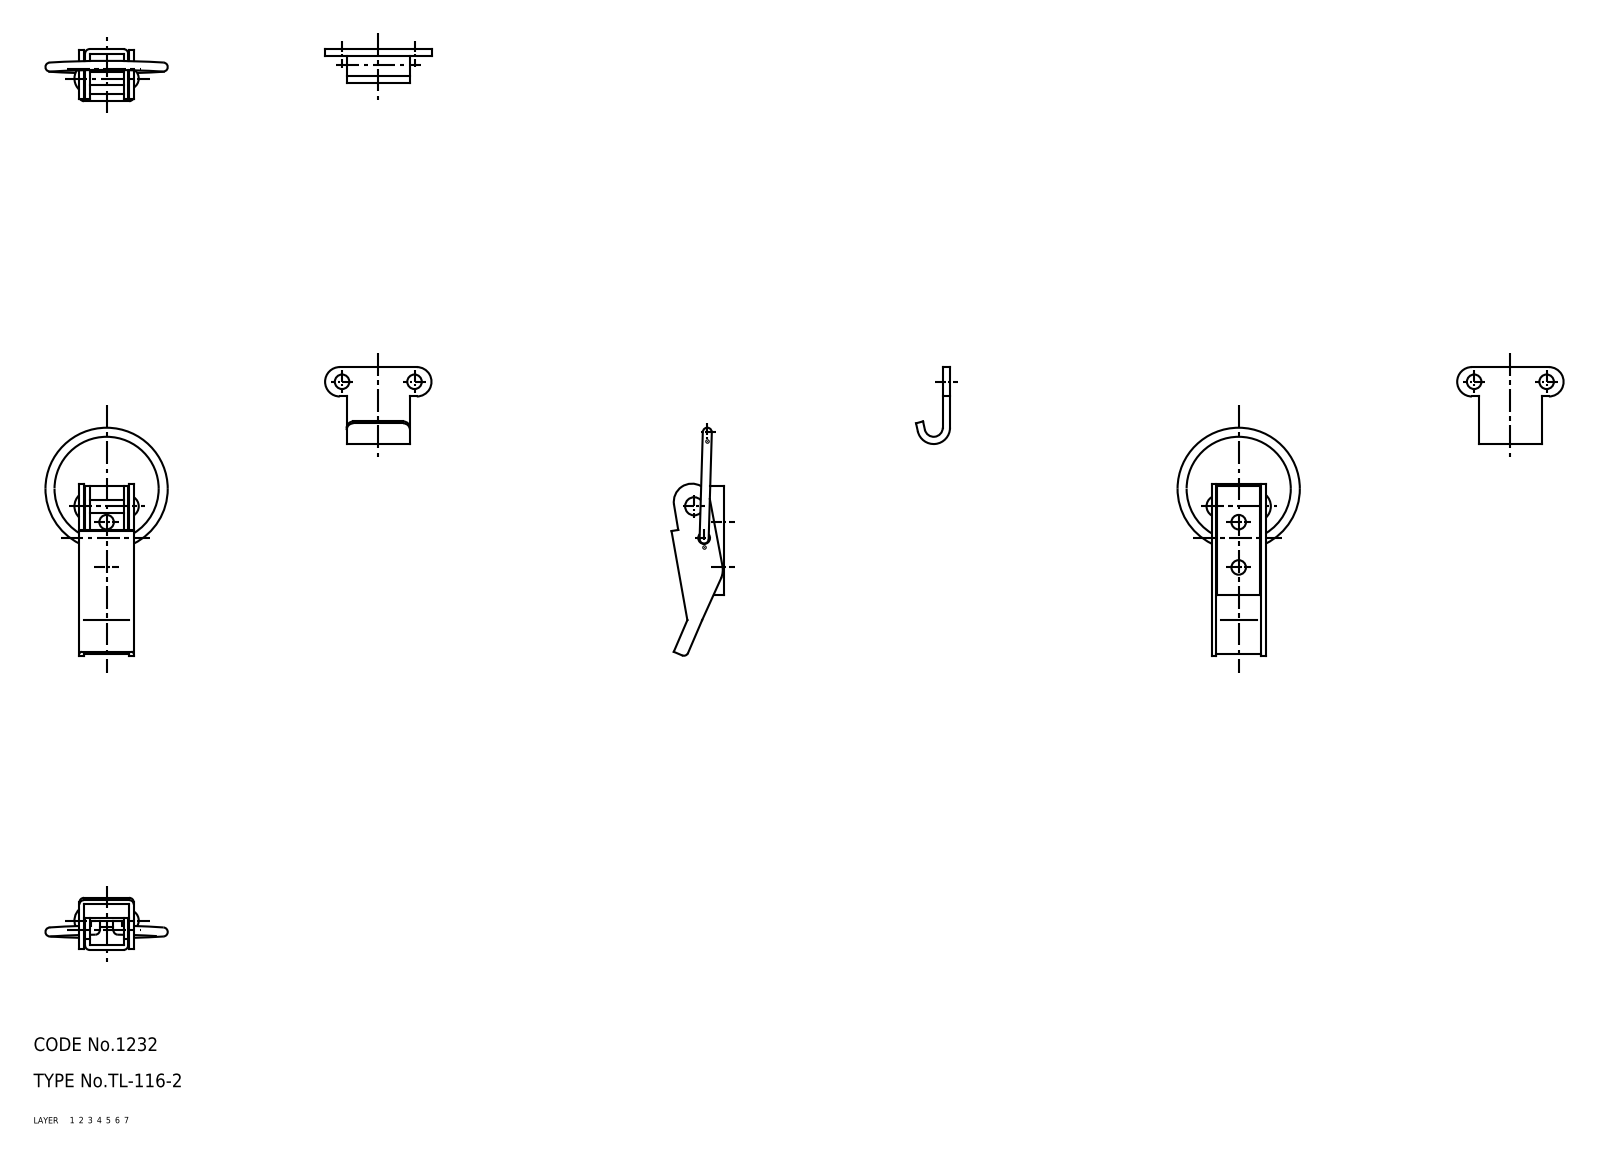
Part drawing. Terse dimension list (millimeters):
name: shaft; lever; keeper; base (+2 more)
written by: CADfix (AUTOMOTIVE_DESIGN)
unit: mm
bodies: 5 solids, 116 faces (0 planar, 0 cylindrical, 116 other)
size: 63.75 × 27 × 11.5
volume: 2 115 mm³; area: 4 241 mm²
